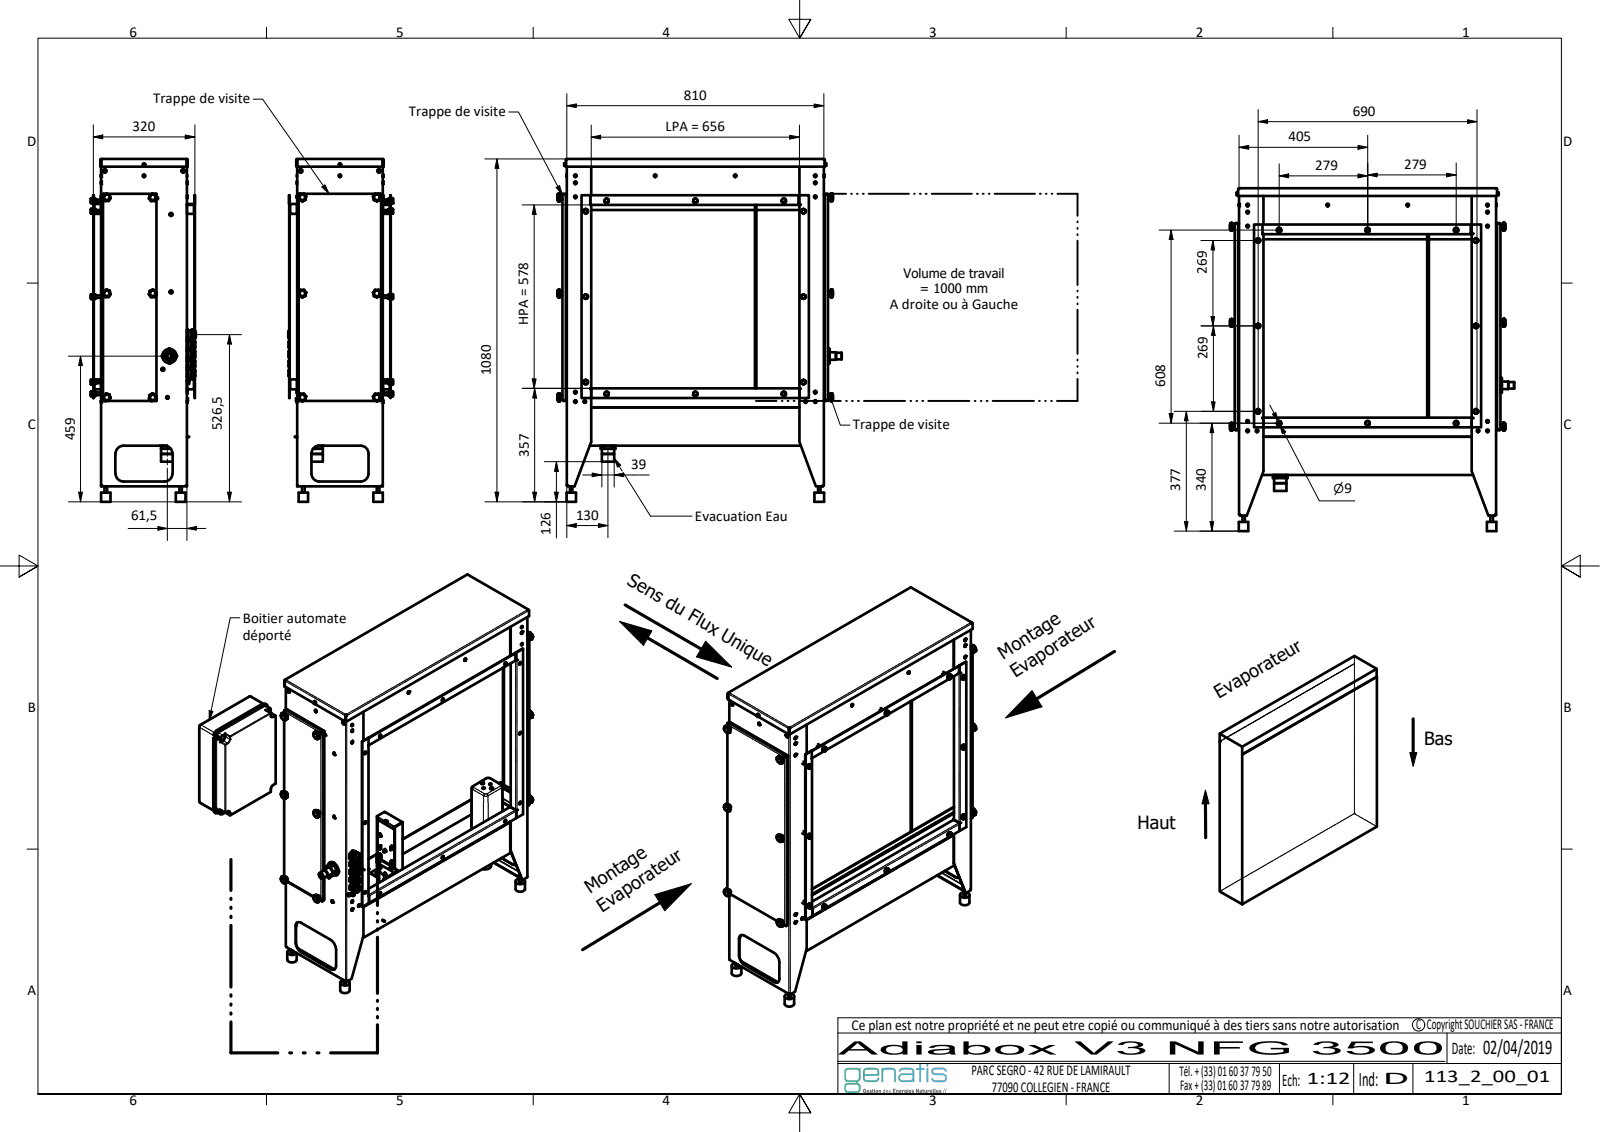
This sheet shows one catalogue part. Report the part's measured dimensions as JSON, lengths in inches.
{"part_name": "113_2_00_01_-_Adiabox_V3; 113_2_00_06_-_Glissiere basse assemblee; 113_3_00_11_-_Cote gauche glissiere; 113_3_00_15_-_Tole de fond pliee (+8 more)", "step_written_by": "Autodesk Inventor 2022 (AUTOMOTIVE_DESIGN)", "units": "inches", "bodies": {"solids": 284, "faces": 8189, "planar": 4196, "cylindrical": 2336, "other": 1657}, "overall_size": [42.52, 35.295, 12.736], "volume_in3": 5739, "surface_area_in2": 15779, "round_holes": [[0.165, 43], [0.236, 42], [0.118, 39], [0.163, 39], [0.354, 15], [0.276, 13], [0.205, 10], [0.039, 8], [0.062, 8], [0.083, 8], [0.087, 8], [0.63, 8]], "round_bosses_or_shafts": [[0.433, 41], [0.311, 39], [0.157, 39], [0.197, 37], [0.276, 34], [0.335, 19], [0.079, 10], [0.138, 8]], "partial_cylinders_radius": [[0.118, 174], [0.059, 89], [0.315, 84], [0.004, 36], [0.012, 36], [0.039, 30], [0.02, 26], [0.079, 21]], "face_to_face_distances": [0.059, 3.937, 0.079, 0.531, 32.362, 0.118, 10.492, 10.433, 0.02, 10.512], "hole_center_spacings": [9.921, 19.843, 29.764, 9.957, 9.966, 10.081, 12.533, 13.131]}
